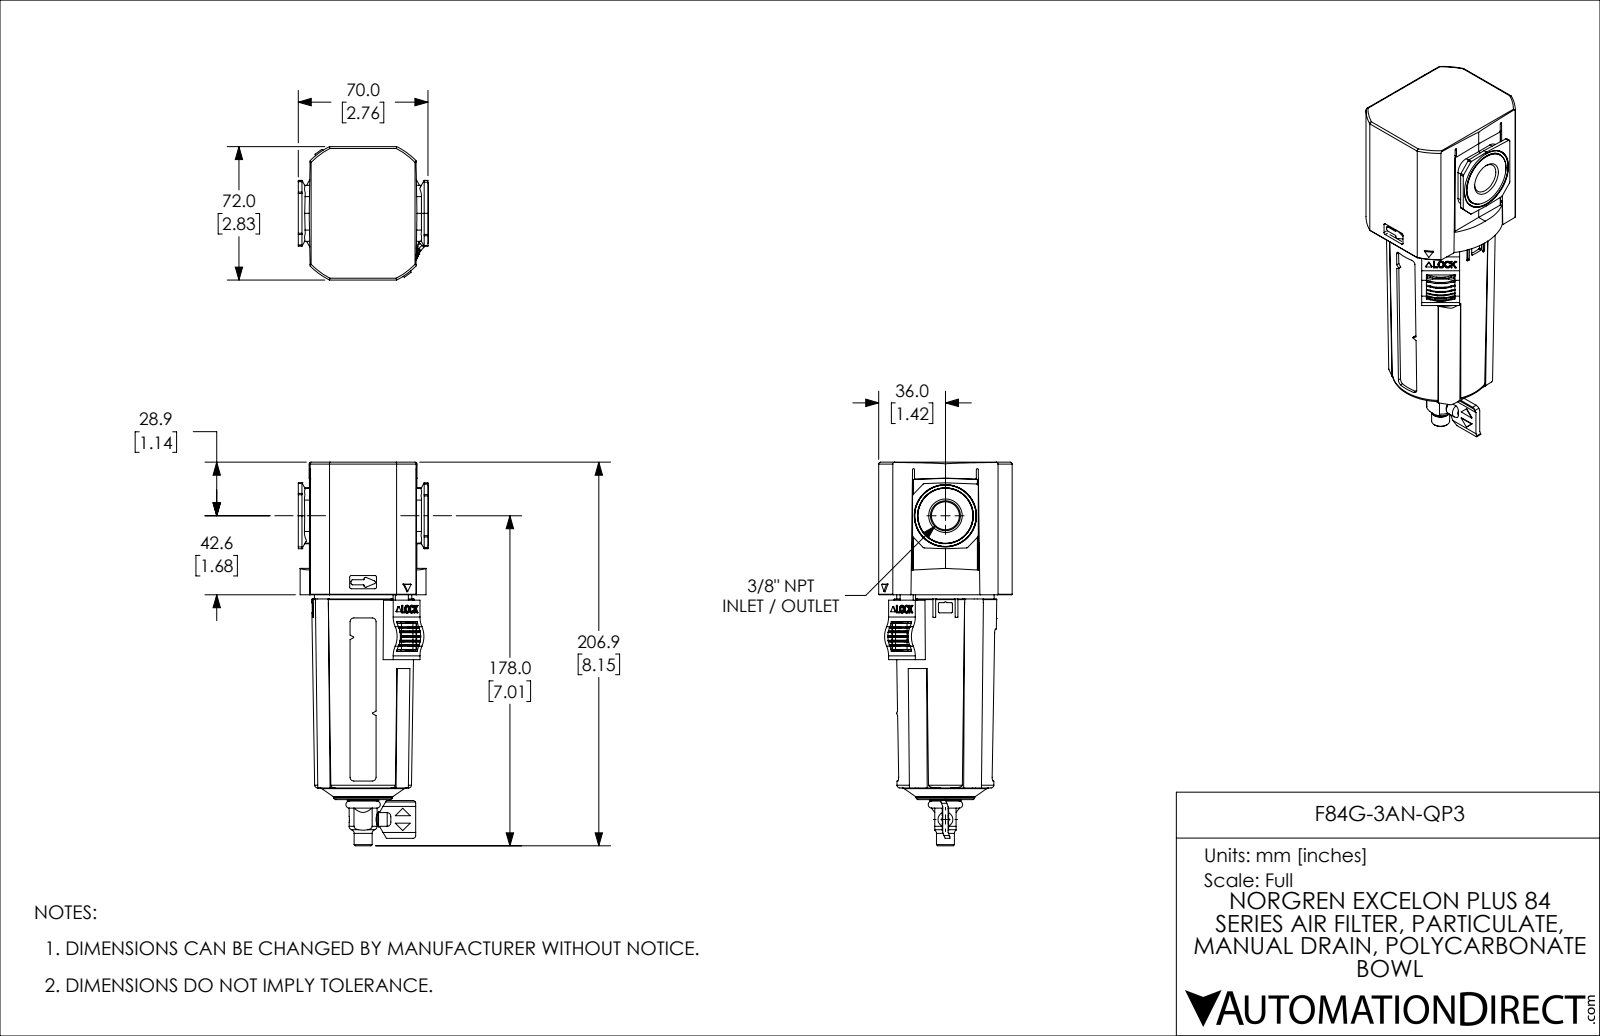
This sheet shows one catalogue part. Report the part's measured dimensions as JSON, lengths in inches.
{"part_name": "F84G-3AN-QP3", "step_written_by": "SolidWorks 2021 (CONFIG_CONTROL_DESIGN)", "units": "inches", "bodies": {"solids": 5, "faces": 1065, "planar": 481, "cylindrical": 382, "other": 202}, "overall_size": [8.146, 2.835, 2.766], "volume_in3": 28.06, "surface_area_in2": 149.3, "round_holes": [[0.163, 2], [0.123, 1], [0.126, 1], [0.236, 1], [0.25, 1], [0.374, 1], [0.969, 1], [2.461, 1]], "round_bosses_or_shafts": [[0.315, 3], [0.276, 2], [0.906, 1], [0.626, 1], [0.399, 1], [0.383, 1], [0.22, 1]], "partial_cylinders_radius": [[0.02, 40], [0.039, 33], [0.01, 24], [0.028, 16], [0.008, 10], [0.038, 8], [0.045, 8], [0.06, 8]], "face_to_face_distances": [0.059, 2.352, 2.411, 2.835, 0.035, 2.317, 2.376, 2.756, 0.404, 0.439], "hole_center_spacings": [0.594, 1.189]}
